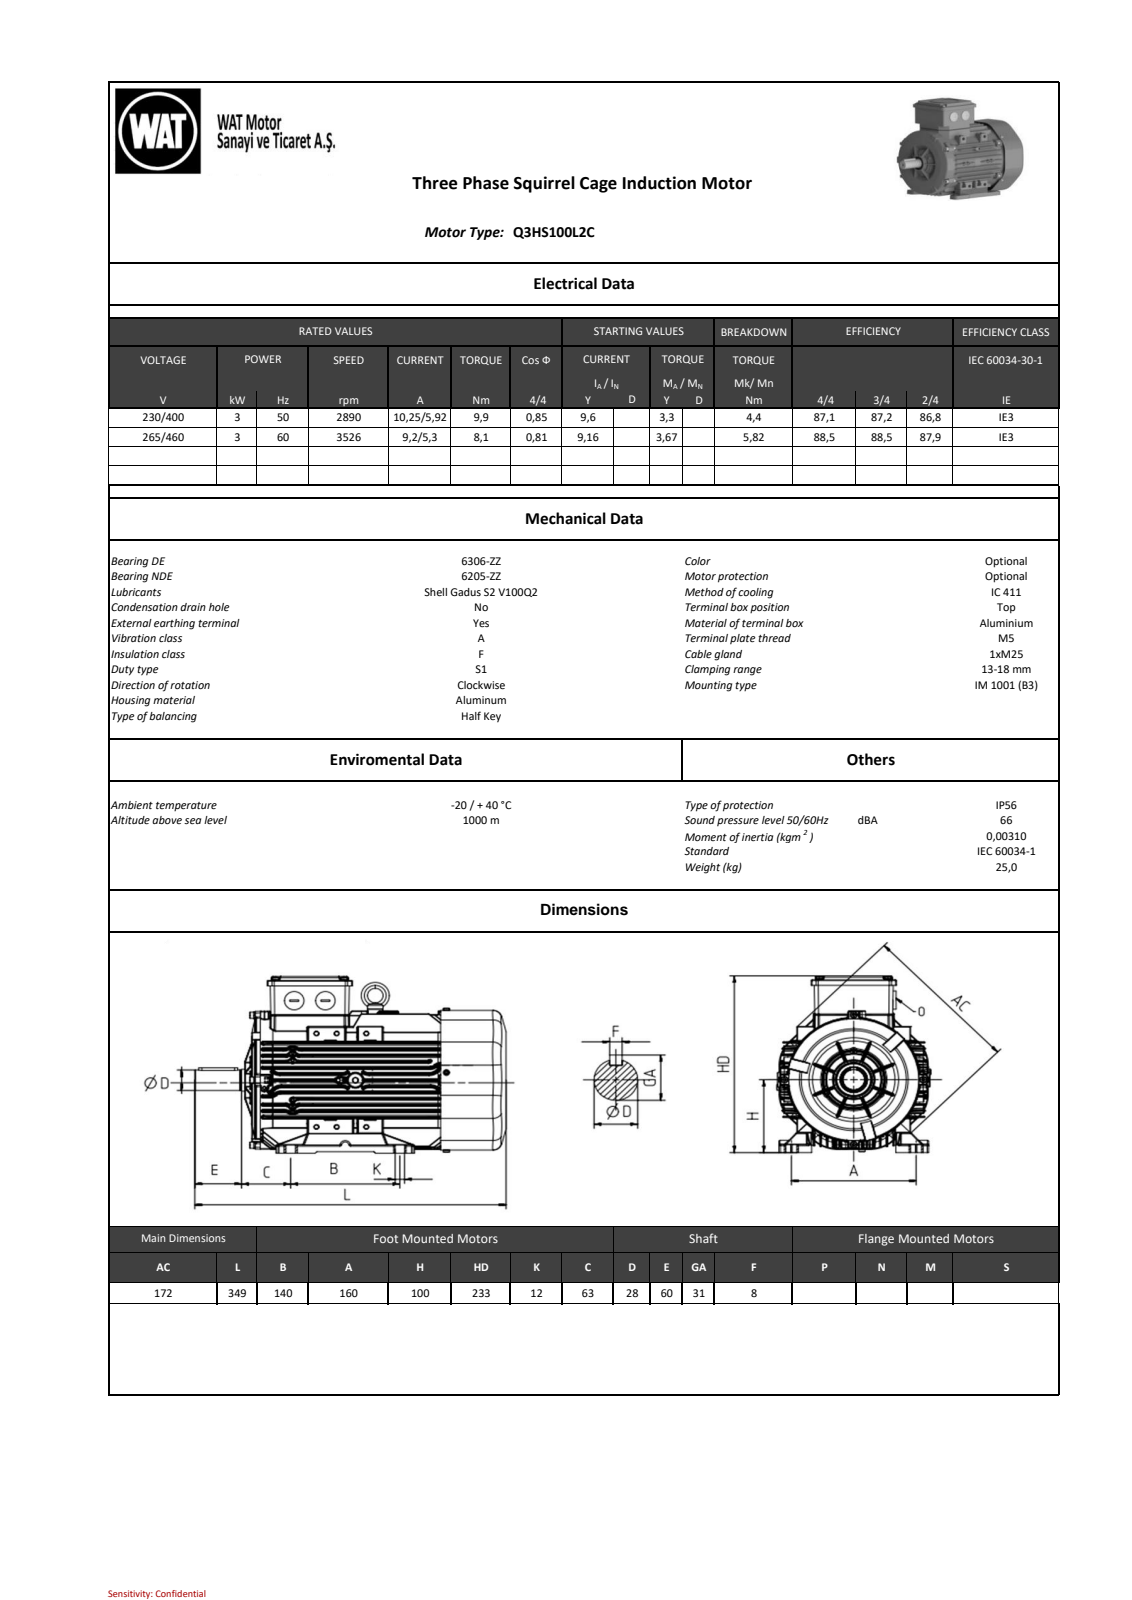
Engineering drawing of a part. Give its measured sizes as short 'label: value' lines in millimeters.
name: QHS series_ 100_B3_stp_objects
written by: SIEMENS PLM Software NX2206.8101 (AUTOMOTIVE_DESIGN)
unit: mm
bodies: 0 solids, 6176 faces (1529 planar, 2787 cylindrical, 1860 other)
size: 349.04 × 233.05 × 185.87
holes: 3× ⌀3.5, 1× ⌀9.87, 1× ⌀79.79, 1× ⌀97.79, 1× ⌀115.78
bosses: 7× ⌀8, 6× ⌀5, 4× ⌀9.6, 4× ⌀9.5, 4× ⌀9.3, 4× ⌀8.5, 2× ⌀25, 1× ⌀102.19
rounds: 650× R1, 560× R0.8, 388× R0.5, 80× R2, 28× R8, 24× R0.6, 11× R0.7, 10× R4
face distances: 7.5, 91.91, 42.5, 8.93, 82.98, 23.57, 206, 7.37, 50.35, 90.35
hole spacings: 67.56, 38.96, 39.01, 39.04, 67.55
